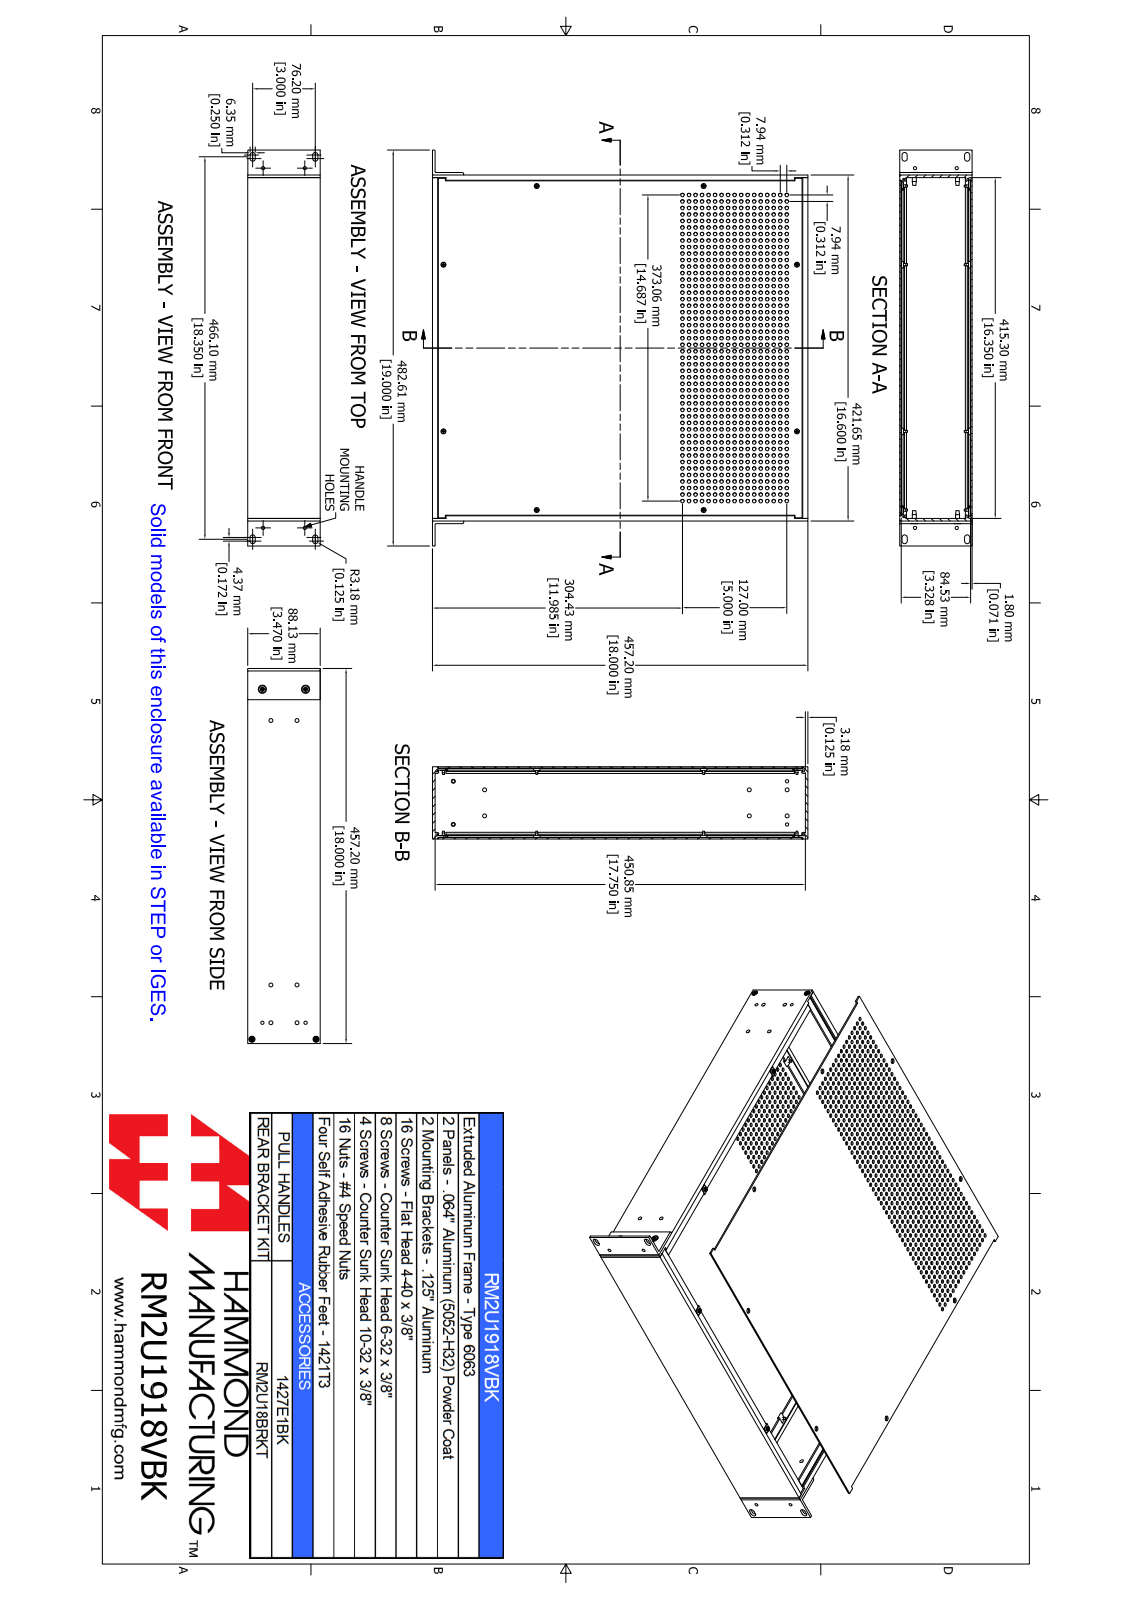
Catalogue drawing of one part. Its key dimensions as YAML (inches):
part_name: "RM2U1918VBK"
step_written_by: "SolidWorks 2021 (AUTOMOTIVE_DESIGN)"
units: inches
bodies: {solids: 52, faces: 2996, planar: 636, cylindrical: 1864, other: 496}
overall_size: [19, 18, 3.471]
volume: 78.09
surface_area: 1846
round_holes:
  - {diameter: 0.17, count: 1632}
  - {diameter: 0.177, count: 16}
  - {diameter: 0.098, count: 8}
  - {diameter: 0.157, count: 8}
  - {diameter: 0.157, count: 8}
  - {diameter: 0.188, count: 6}
  - {diameter: 0.159, count: 4}
  - {diameter: 0.169, count: 4}
  - {diameter: 0.169, count: 4}
  - {diameter: 0.197, count: 4}
round_bosses_or_shafts:
  - {diameter: 0.214, count: 16}
  - {diameter: 0.112, count: 16}
  - {diameter: 0.333, count: 4}
  - {diameter: 0.238, count: 4}
  - {diameter: 0.19, count: 4}
  - {diameter: 0.138, count: 4}
partial_cylinders:
  - {radius: 0.125, count: 16}
  - {radius: 0.039, count: 14}
  - {radius: 0.049, count: 8}
  - {radius: 0.05, count: 8}
  - {radius: 0.038, count: 6}
  - {radius: 0.037, count: 5}
  - {radius: 0.079, count: 2}
face_to_face_distances: [0.071, 3.399, 3.47, 3.328, 0.125, 0.125, 16.6, 16.476, 16.35, 18]
hole_center_spacings: [1.25, 0.313, 0.937, 1.563, 8, 0.625, 2.5, 13.031]
